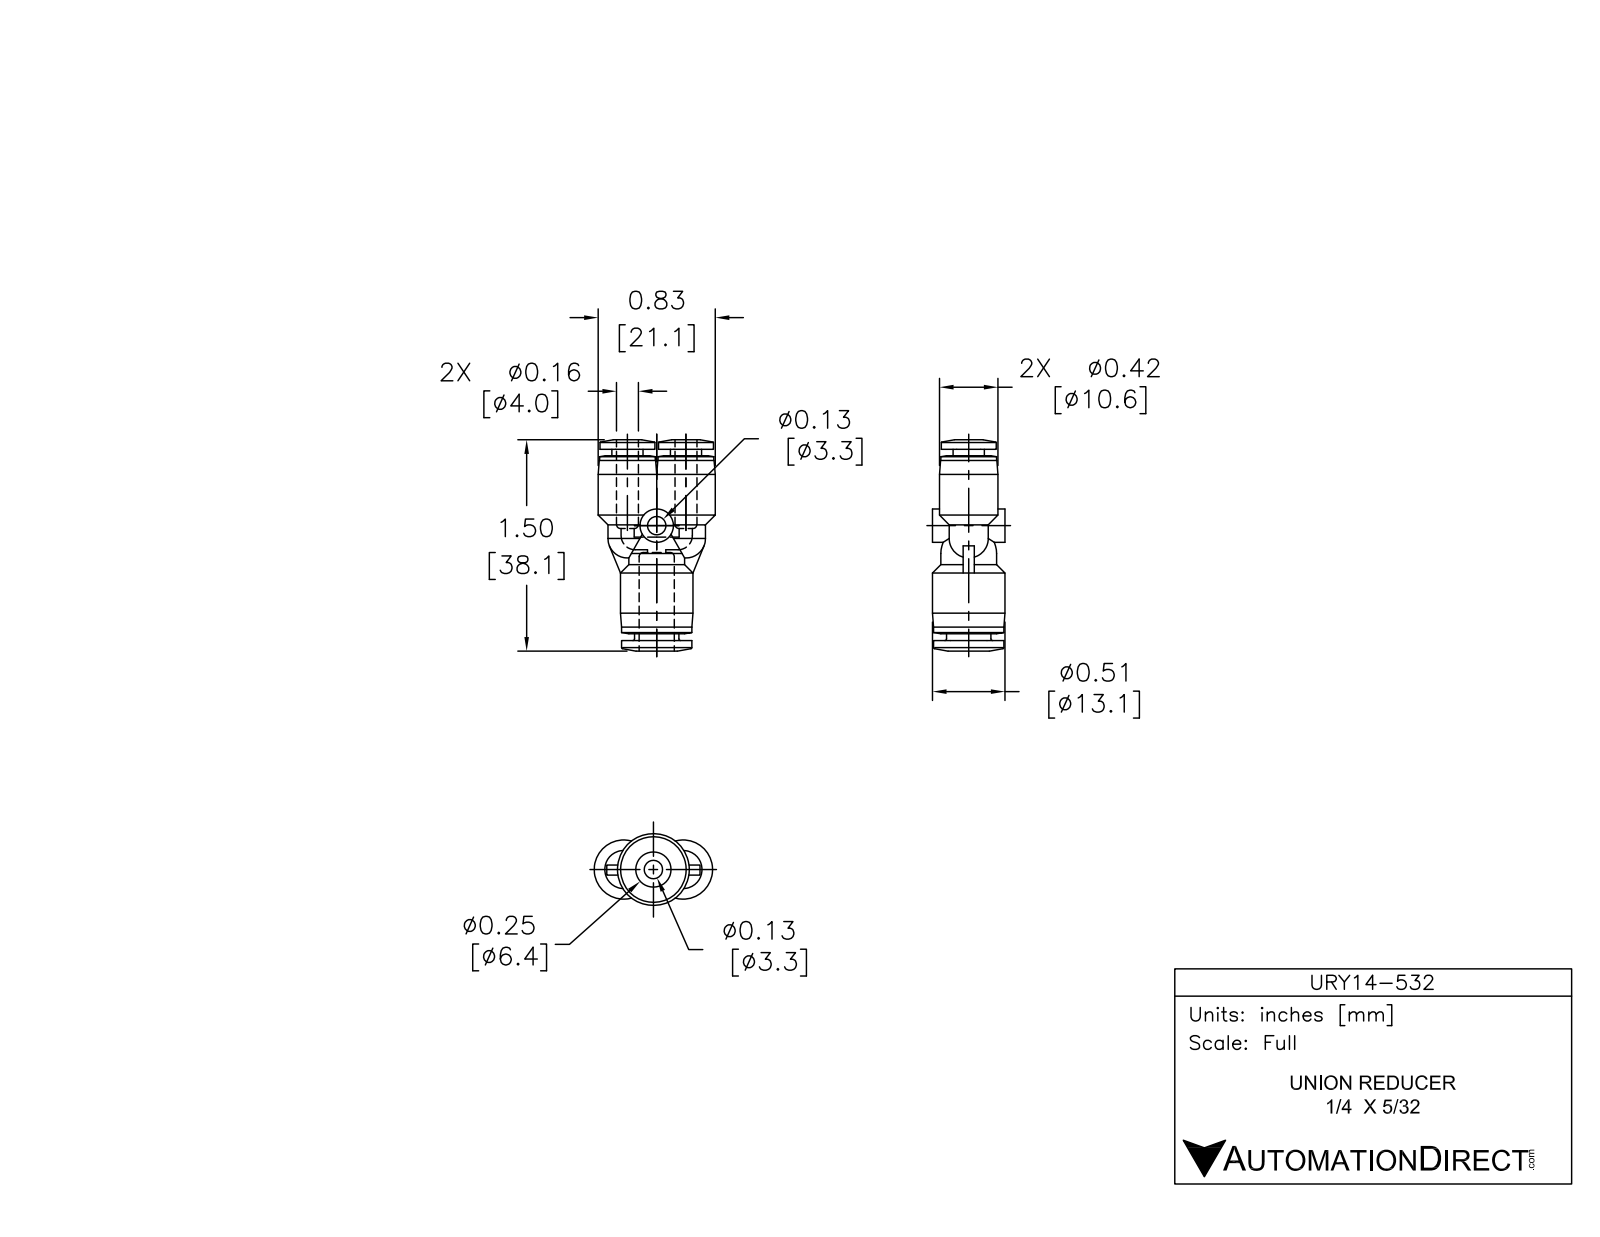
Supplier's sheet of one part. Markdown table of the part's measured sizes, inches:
| quantity | value |
| --- | --- |
| part name | URY14-532 |
| STEP written by | SolidWorks 2015 (AUTOMOTIVE_DESIGN) |
| units | inches |
| bodies | 1 solid, 112 faces (18 planar, 41 cylindrical, 53 other) |
| overall size | 1.492 × 0.827 × 0.512 |
| volume | 0.237 in³ |
| surface area | 5.49 in² |
| round holes (diameter × count) | 0.169 × 2, 0.13 × 1, 0.258 × 1 |
| round bosses / shafts (diameter × count) | 0.394 × 3, 0.413 × 2, 0.388 × 2, 0.22 × 2, 0.512 × 1, 0.496 × 1, 0.313 × 1, 0.236 × 1 |
| partial cylindrical surfaces (radius × count) | 0.138 × 2 |
| main face-to-face distances | 1.35, 1.305, 0.045, 0.047, 1.258, 1.303, 0.217, 0.295, 0.63, 0.583 |
| hole center spacings | 0.207, 0.413 |
